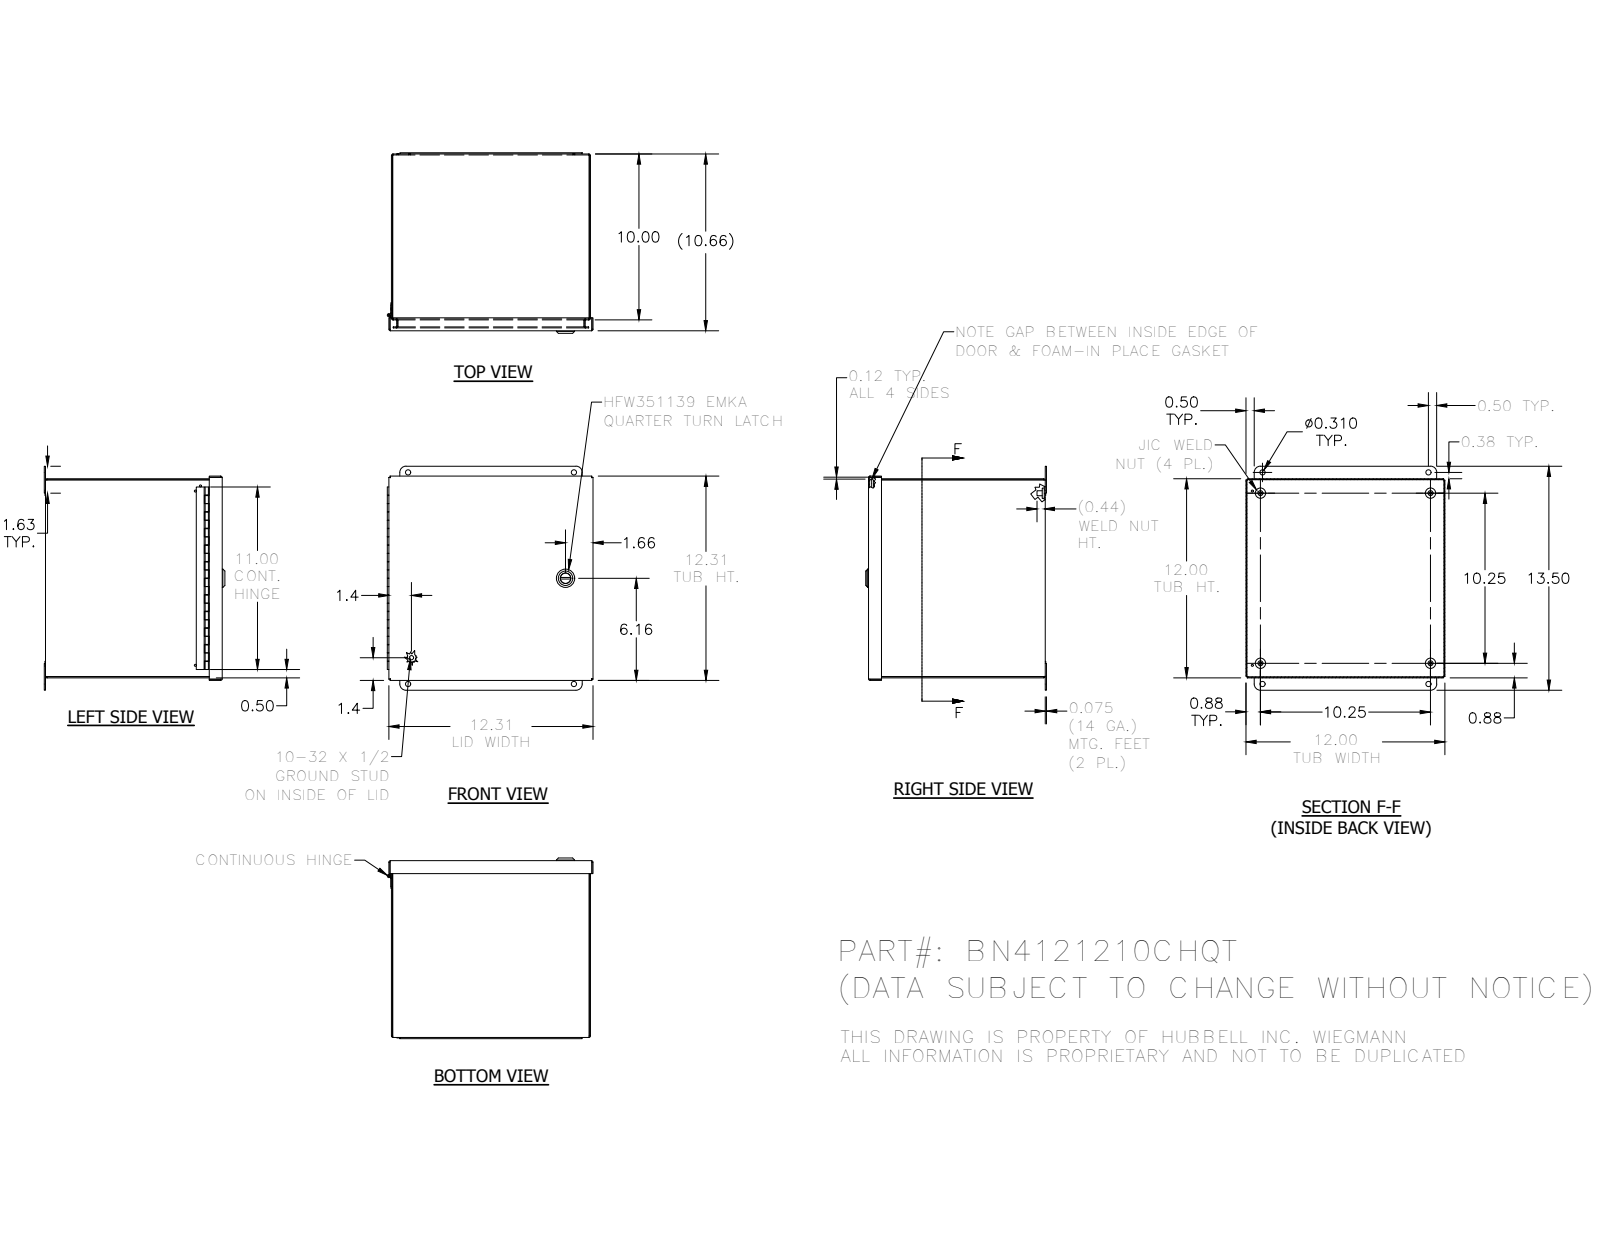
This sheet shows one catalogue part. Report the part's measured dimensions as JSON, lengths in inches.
{"part_name": "BN4121210CHQT", "step_written_by": "SolidWorks 2018 (AUTOMOTIVE_DESIGN)", "units": "inches", "bodies": {"solids": 21, "faces": 809, "planar": 408, "cylindrical": 273, "other": 128}, "overall_size": [13.5, 12.406, 10.888], "volume_in3": 61.1, "surface_area_in2": 1890, "round_holes": [[0.12, 9], [0.156, 4], [0.31, 4], [0.116, 1], [0.197, 1], [0.315, 1], [0.394, 1], [0.402, 1], [0.634, 1], [0.802, 1]], "round_bosses_or_shafts": [[0.625, 4], [0.3, 4], [1.102, 1], [0.866, 1], [0.78, 1], [0.622, 1], [0.598, 1], [0.531, 1]], "partial_cylinders_radius": [[0.012, 30], [0.031, 20], [0.093, 20], [0.125, 16], [0.02, 12], [0.157, 4], [0.375, 4], [0.016, 2]], "face_to_face_distances": [0.062, 11.938, 0.062, 12, 10.594, 10.656, 10.532, 10.594, 11.876, 11.938], "hole_center_spacings": [10.25, 10.68, 15.322, 0.737, 1.256, 5.09, 9.907, 9.993]}
